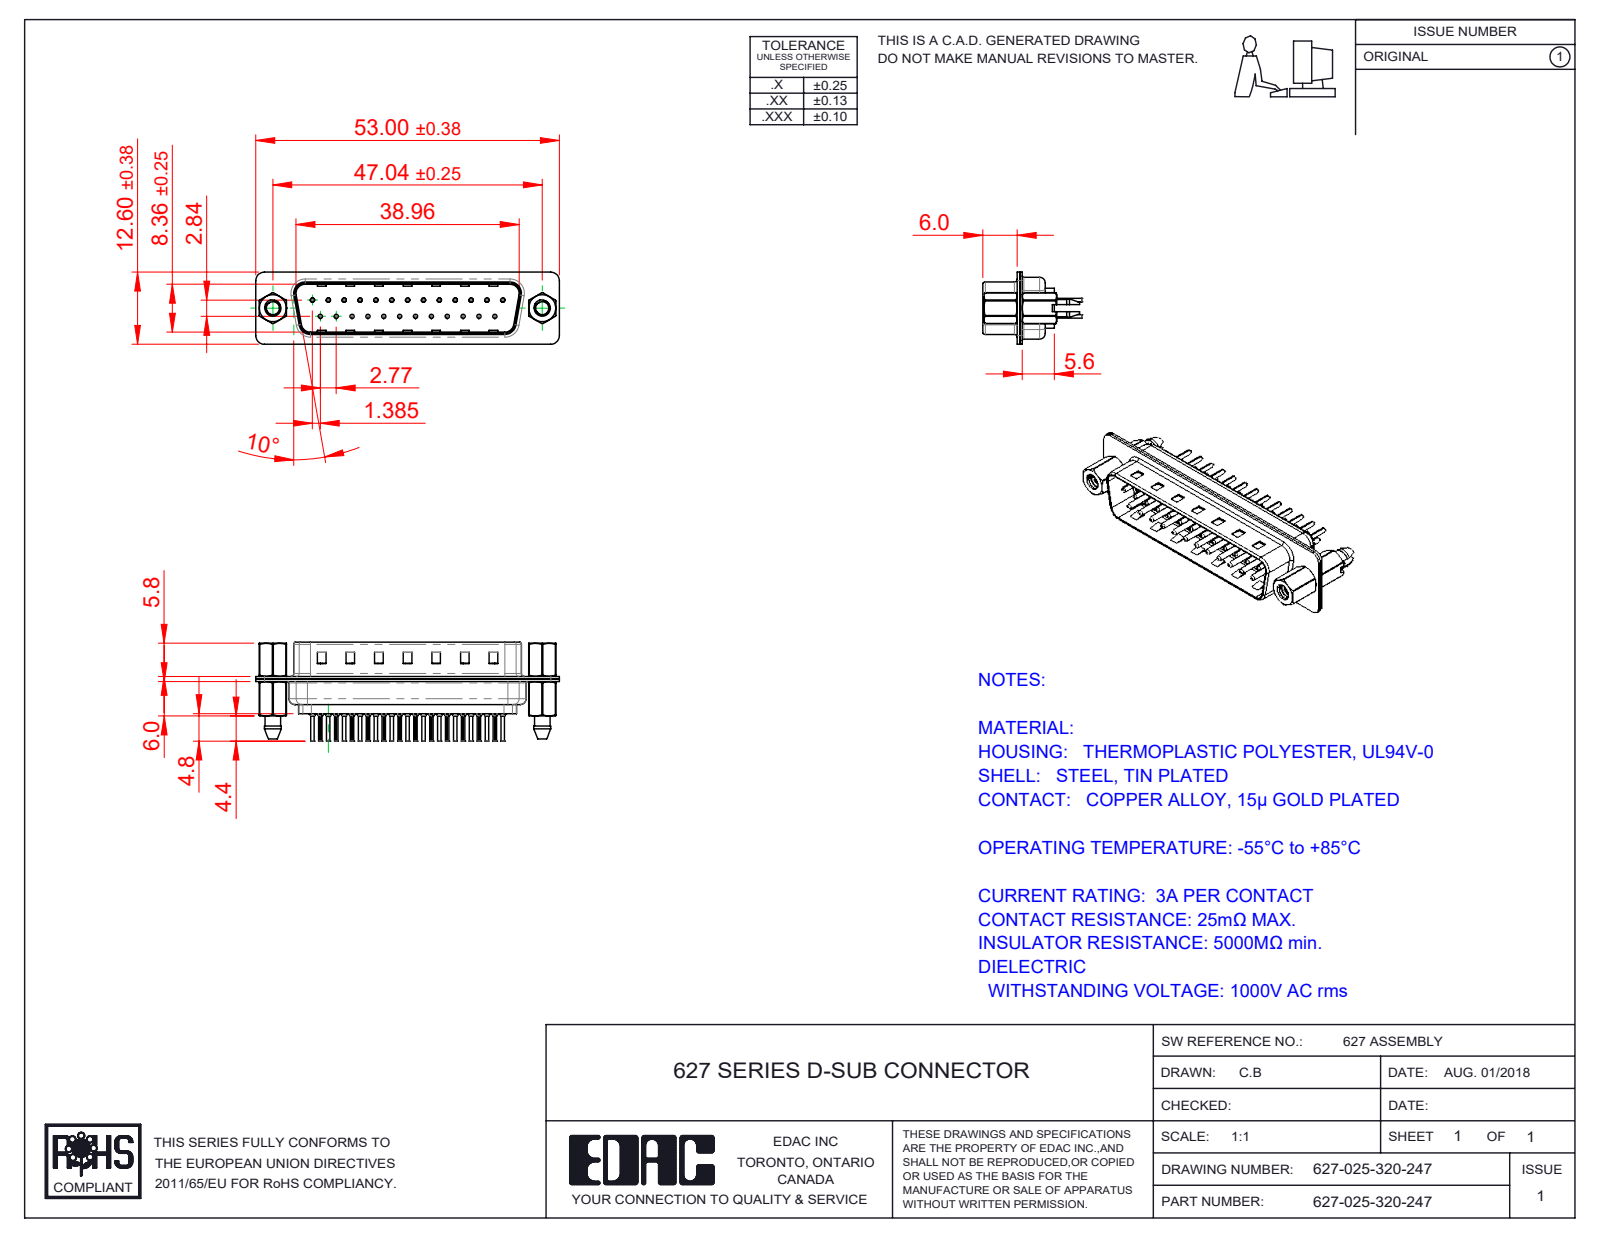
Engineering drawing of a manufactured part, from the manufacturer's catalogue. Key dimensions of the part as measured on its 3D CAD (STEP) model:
Part name (STEP PRODUCT): 627-025-320-047; 627 4-40 Hex Standoff; 627 Contact Row 2_20L; 627 Contact Row 1_20L (+4 more)
STEP written by: SolidWorks 2020 (CONFIG_CONTROL_DESIGN)
Units: millimetres
Bodies: 32 solids, 3026 faces (825 planar, 1166 cylindrical, 1035 other)
Overall size (bounding box): 53 × 17.3 × 12.6
Volume: 3 009 mm³ · Surface area: 8 578 mm²
Round holes (diameter × count): ⌀0.2 ×25, ⌀0.35 ×25, ⌀1.1 ×25, ⌀1.6 ×25, ⌀2.26 ×2, ⌀2.29 ×2, ⌀4 ×2, ⌀4.8 ×2
Round bosses / shafts (diameter × count): ⌀2 ×25, ⌀1.5 ×25, ⌀0.75 ×25, ⌀0.6 ×25, ⌀4.9 ×2, ⌀2.79 ×2
Partial cylindrical surfaces — rounded edges, fillets, slot ends (radius × count): R0.1 ×50, R1.5 ×18, R2 ×12, R1.6 ×10, R0.5 ×8, R0.25 ×4, R0.6 ×4, R0.65 ×4
Main face-to-face distances: 0.4, 0.45, 0.82, 9.58, 8.76, 0.9, 1.5, 1.4, 6.5, 6.05
Hole centre spacings: 3.16, 8.31, 2.77, 5.54, 11.08, 16.62, 5.03, 5.04
